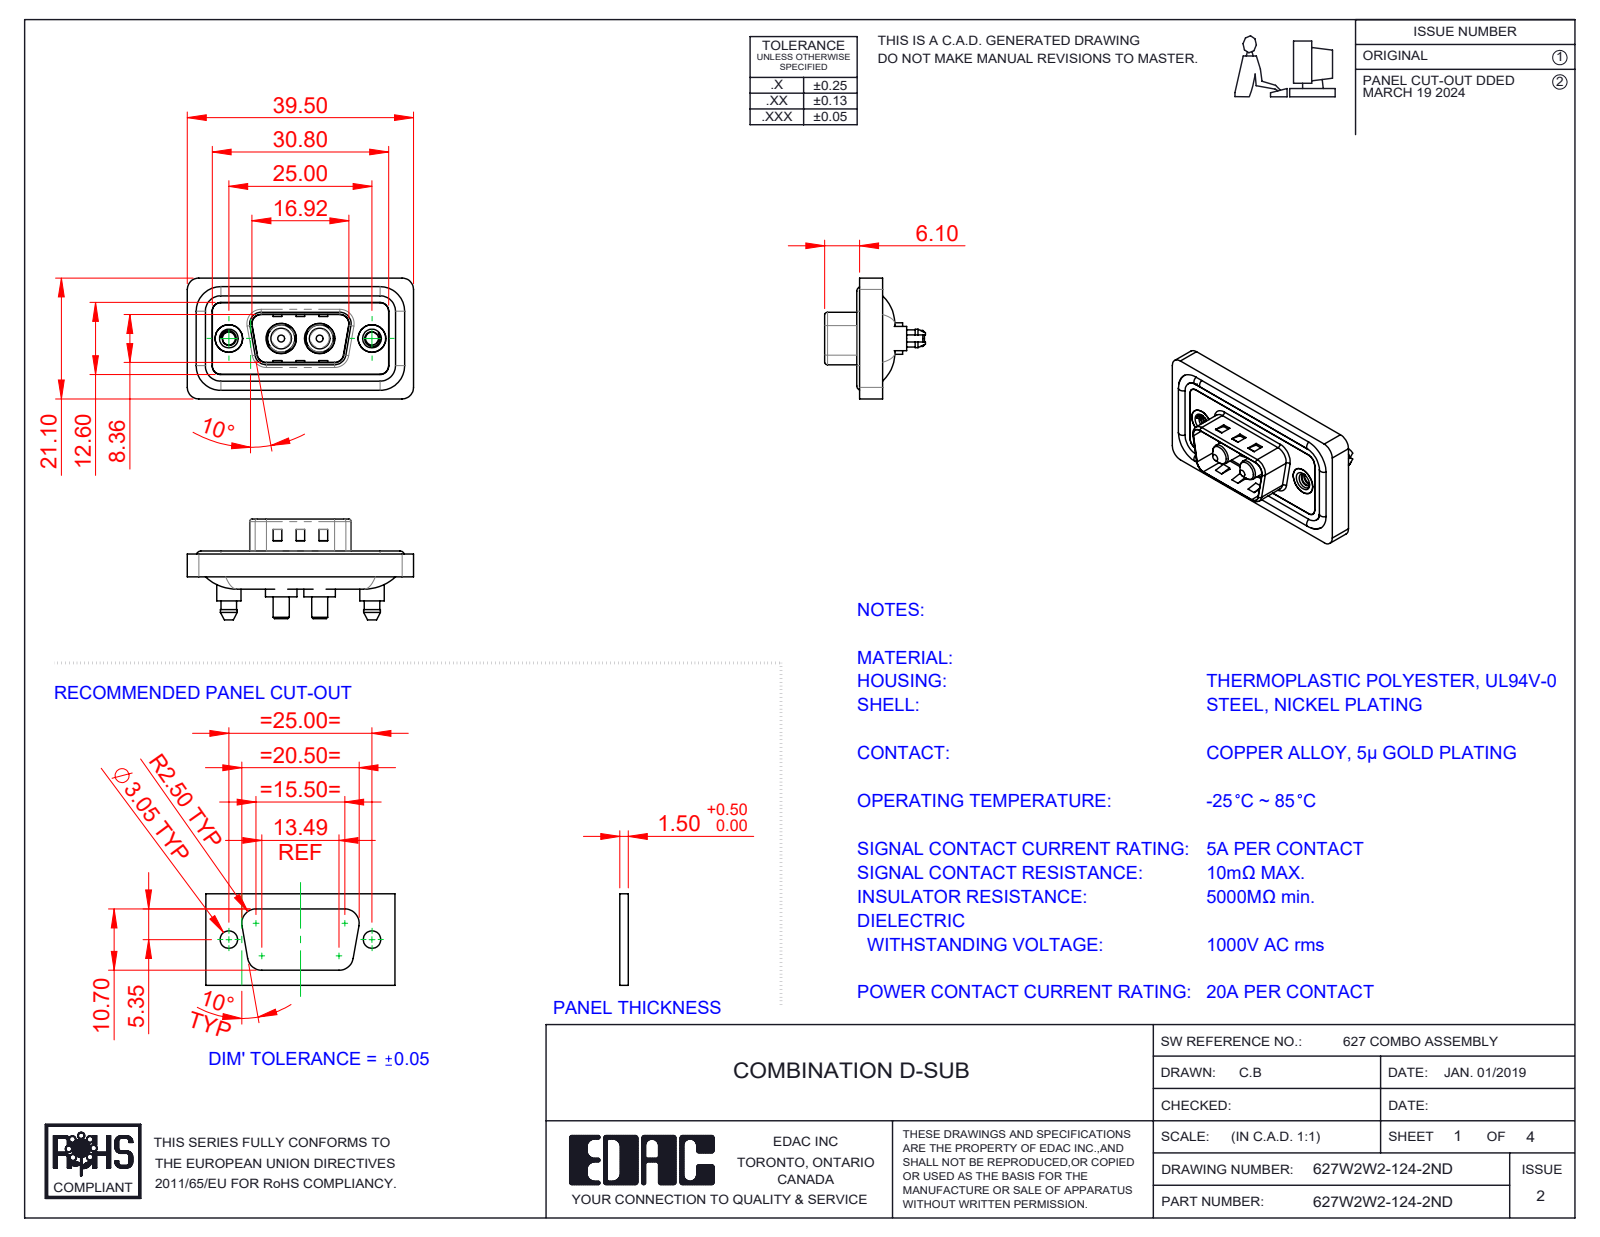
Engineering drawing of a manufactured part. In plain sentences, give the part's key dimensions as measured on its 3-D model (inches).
The part is named "627Combo Shell Front_09 Contacts; 627Combo Threaded Boardlock_D; 627Combo Shell Rear_09 Contacts; 627Combo Waterproof Housing_09 Contacts (+4 more)". Its 3-D file was written by "SolidWorks 2023 (CONFIG_CONTROL_DESIGN)". It is 11 solids with 547 faces: 181 planar, 258 cylindrical and 108 other. Overall it measures 1.555 by 0.831 by 0.693 inches. Its volume is 0.28 cubic inches and its surface area 11.35 square inches. Round holes: 2 of diameter 0.089, 2 of diameter 0.157, 2 of diameter 0.189, 2 of diameter 0.191, 2 of diameter 0.197, 2 of diameter 0.209. Round bosses or shafts: 4 of diameter 0.063, 2 of diameter 0.217, 2 of diameter 0.213, 2 of diameter 0.205, 2 of diameter 0.193, 2 of diameter 0.187, 2 of diameter 0.167, 2 of diameter 0.148. Partial cylindrical surfaces (rounded edges, fillets, slot ends): 24 of radius 0.059, 18 of radius 0.079, 10 of radius 0.063, 8 of radius 0.02, 4 of radius 0.01, 4 of radius 0.024, 4 of radius 0.026, 4 of radius 0.035. The main face-to-face distances are 0.016, 0.043, 0.114, 0.122, 0.02, 0.063, 0.059, 0.157, 0.028, 0.098. The hole center spacings are 0.36, 0.624, 0.265, 0.984.
